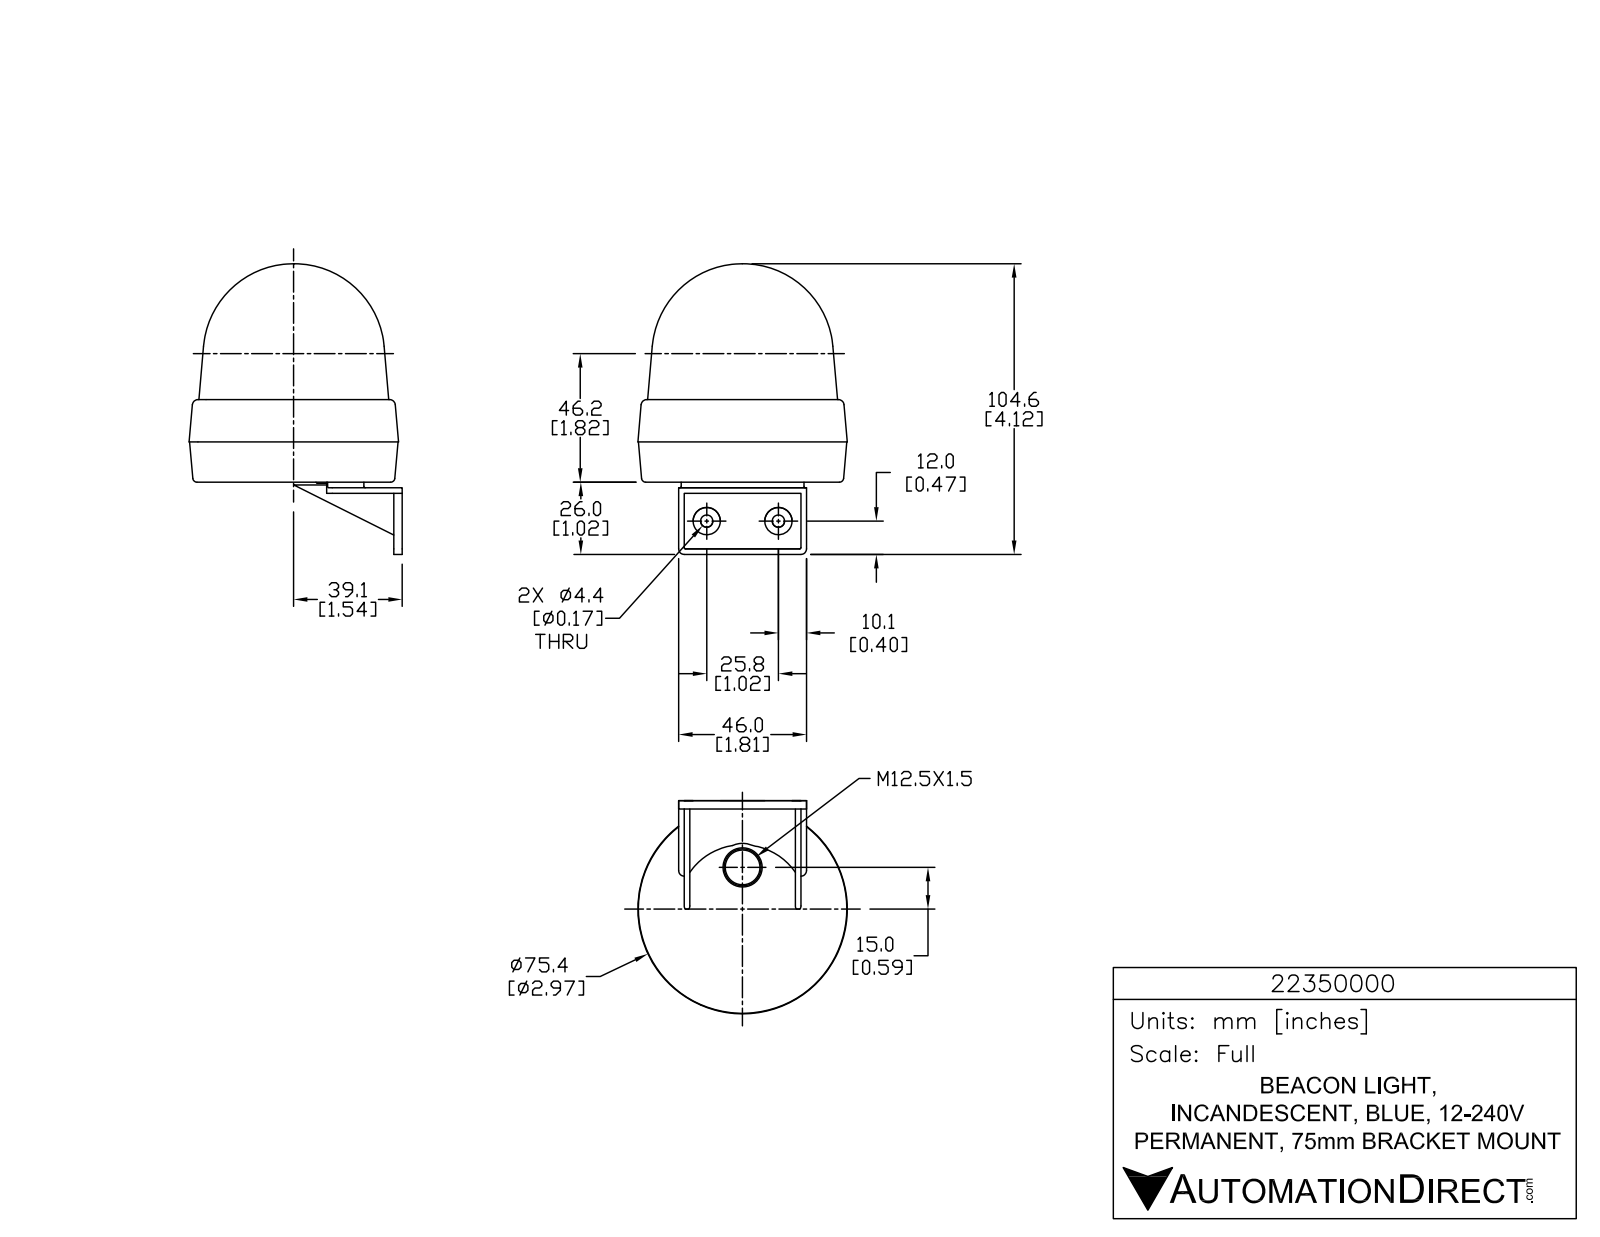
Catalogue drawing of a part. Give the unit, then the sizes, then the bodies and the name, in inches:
Units: inches
Overall size (bounding box): 4.117 × 3.253 × 2.967
Round holes (diameter × count): ⌀0.059 ×3, ⌀0.173 ×2
Round bosses / shafts (diameter × count): ⌀0.339 ×3, ⌀0.084 ×3, ⌀0.386 ×2
Partial cylindrical surfaces — rounded edges, fillets, slot ends (radius × count): R0.005 ×9, R0.005 ×6, R0.012 ×6, R0.012 ×6, R0.012 ×6, R0.02 ×6, R0.196 ×6, R0.079 ×4
Main face-to-face distances: 0.079, 0.157, 1.574, 0.039, 0.118, 1.653, 1.496, 0.079, 1.654, 1.732
Hole centre spacings: 1.016
Volume: 16.02 in³ · Surface area: 41.97 in²
Bodies: 1 solid, 819 faces (549 planar, 180 cylindrical, 90 other)
Part name (STEP PRODUCT): 22350000
STEP written by: SolidWorks 2015 (AUTOMOTIVE_DESIGN)
